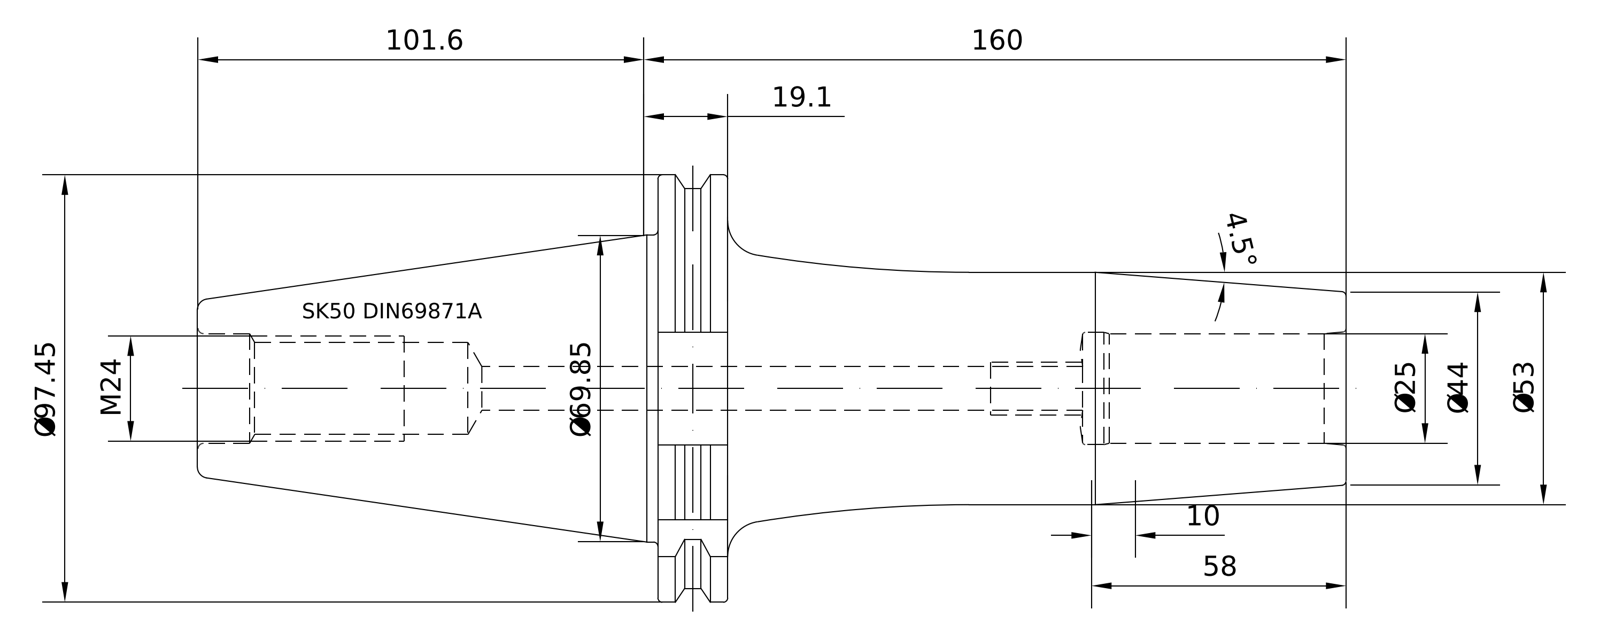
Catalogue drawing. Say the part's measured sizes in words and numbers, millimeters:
The part is named "50-442-25". Its 3-D file was written by "PRO/ENGINEER BY PARAMETRIC TECHNOLOGY CORPORATION, 2010430 (CONFIG_CONTROL_DESIGN)". It is 1 solid with 96 faces: 22 planar, 24 cylindrical and 50 other. Overall it measures 261.6 by 97.47 by 94 millimeters. Its volume is 619 825 cubic millimeters and its surface area 68 445 square millimeters. Round holes: 1 of diameter 20.75, 1 of diameter 25, 1 of diameter 25.01, 1 of diameter 25.7. Round bosses or shafts: 1 of diameter 91, 1 of diameter 69.15, 1 of diameter 53, 1 of diameter 24.01. Partial cylindrical surfaces (rounded edges, fillets, slot ends): 1 of radius 1.75, 1 of radius 48.74. The main face-to-face distances are 15.85, 156.8, 140.95, 98.8, 82.95, 58, 72.8, 104.8, 120.65, 203.6.
